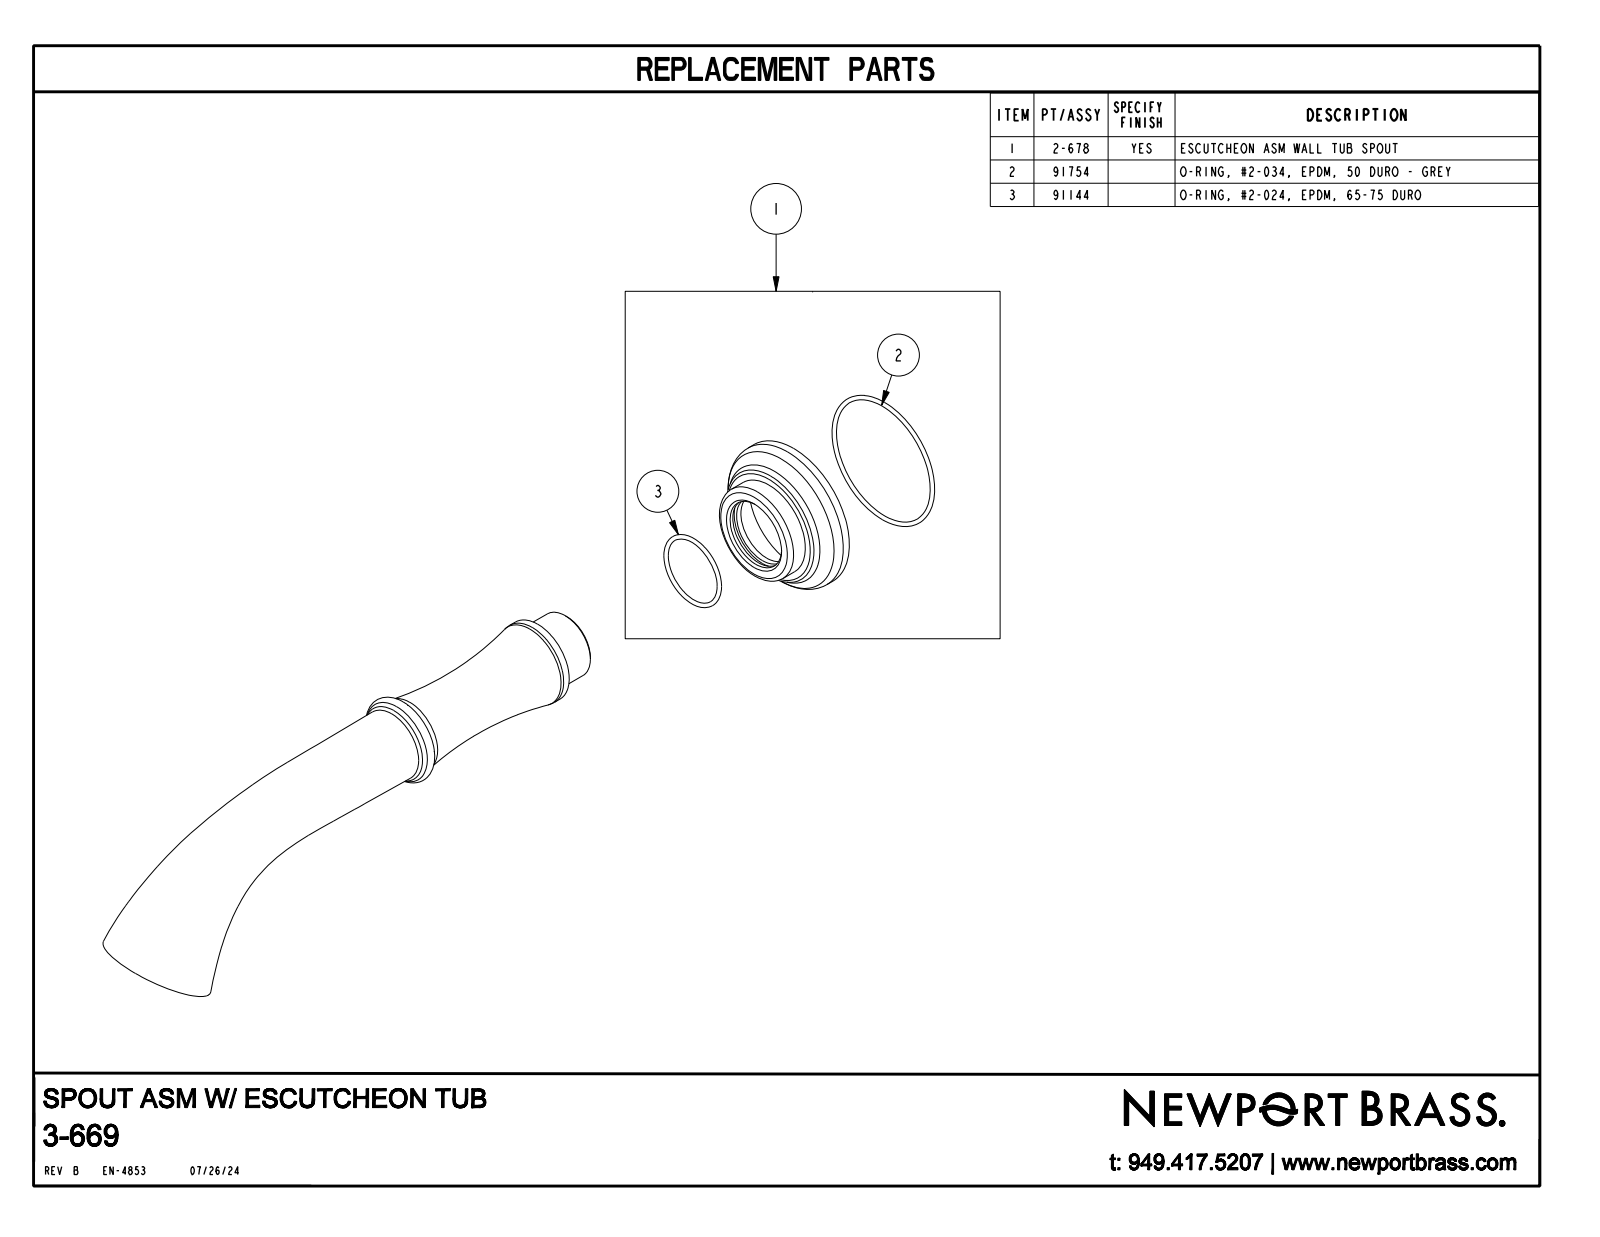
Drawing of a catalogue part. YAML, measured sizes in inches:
part_name: "3-669"
step_written_by: "CREO PARAMETRIC BY PTC INC, 2018400 (AUTOMOTIVE_DESIGN)"
units: inches
bodies: {solids: 1, faces: 78, planar: 8, cylindrical: 14, other: 56}
overall_size: [9.83, 3.028, 2.48]
volume: 13.46
surface_area: 50.96
round_holes:
  - {diameter: 1.063, count: 1}
round_bosses_or_shafts:
  - {diameter: 2.48, count: 1}
  - {diameter: 1.62, count: 1}
  - {diameter: 1.4, count: 1}
  - {diameter: 1.034, count: 1}
  - {diameter: 1.033, count: 1}
  - {diameter: 0.936, count: 1}
face_to_face_distances: [0.55, 0.88, 0.33, 4.24, 3.69, 3.36, 4.155, 3.605, 3.275, 0.085]
